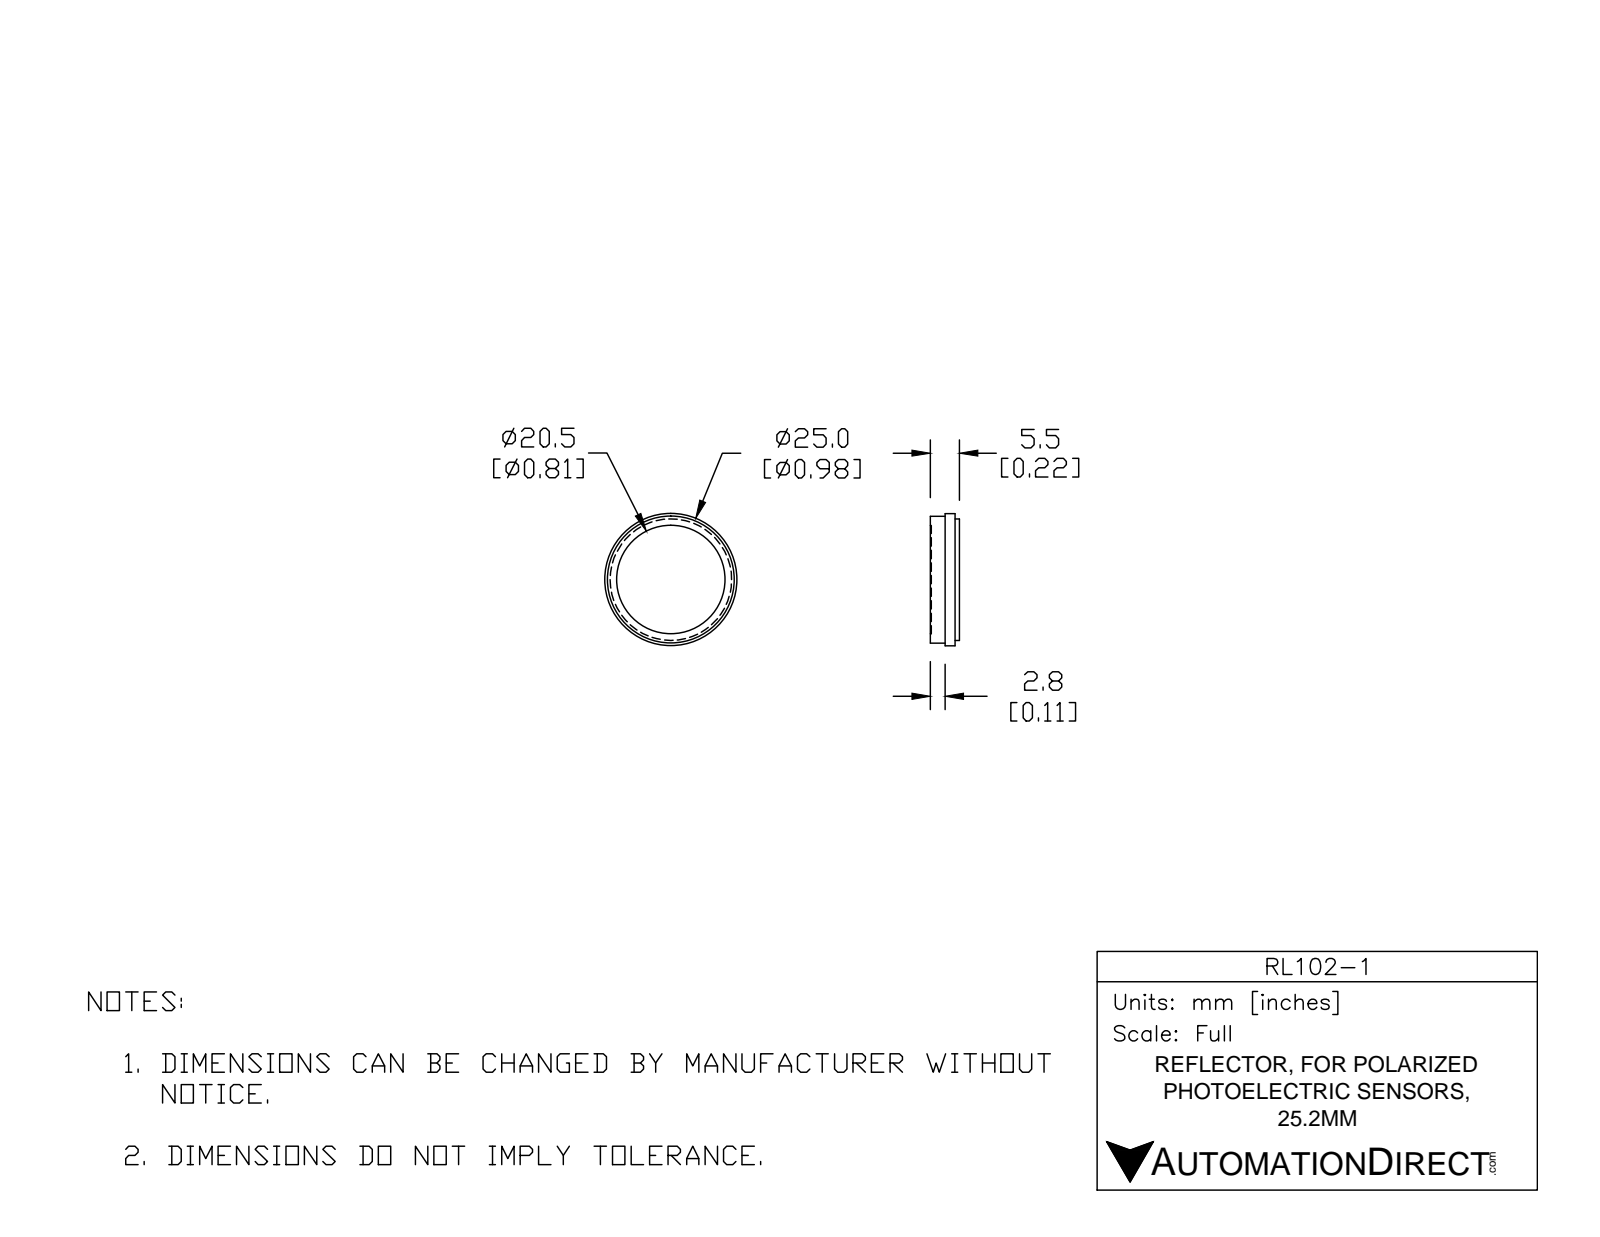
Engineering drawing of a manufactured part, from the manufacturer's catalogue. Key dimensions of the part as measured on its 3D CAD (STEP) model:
Part name (STEP PRODUCT): RL-102-1
STEP written by: SolidWorks 2017 (AUTOMOTIVE_DESIGN)
Units: inches
Bodies: 1 solid, 13 faces (5 planar, 8 cylindrical, 0 other)
Overall size (bounding box): 0.984 × 0.984 × 0.217
Volume: 0.15 in³ · Surface area: 2.19 in²
Round holes (diameter × count): ⌀0.807 ×1
Round bosses / shafts (diameter × count): ⌀0.984 ×1, ⌀0.945 ×1, ⌀0.906 ×1
Main face-to-face distances: 0.209, 0.217, 0.031, 0.177, 0.185, 0.106, 0.075, 0.102, 0.11
